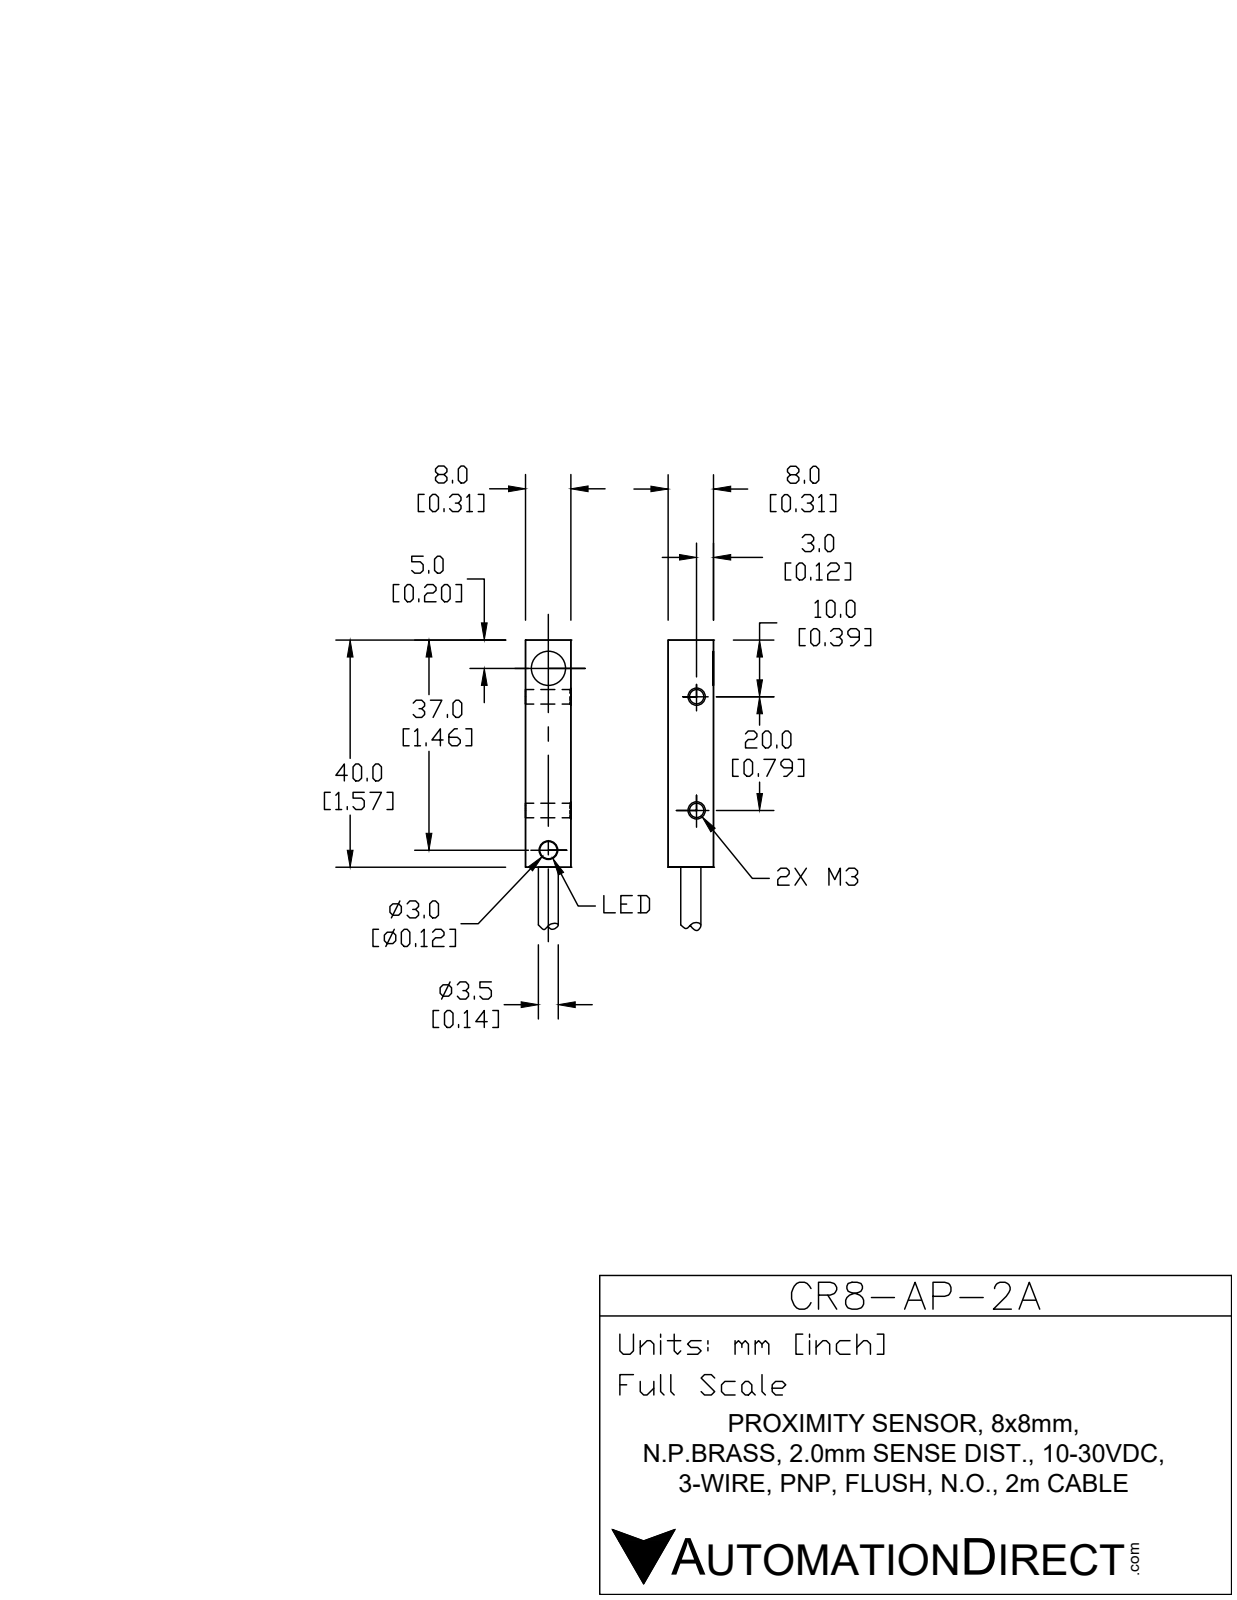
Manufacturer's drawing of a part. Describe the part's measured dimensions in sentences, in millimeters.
The part is named "CR8-AP-2A". Its 3-D file was written by "SolidWorks 2017 (AUTOMOTIVE_DESIGN)". It is 3 solids with 30 faces: 19 planar, 4 cylindrical and 7 other. Overall it measures 61.9 by 8 by 8 millimeters. Its volume is 2 870 cubic millimeters and its surface area 2 534 square millimeters. Round holes: 2 of diameter 2.5. Round bosses or shafts: 1 of diameter 3.5. Partial cylindrical surfaces (rounded edges, fillets, slot ends): 1 of radius 3.4. The main face-to-face distances are 8, 0.5, 7.5, 7.9, 0.4, 40, 7.4, 7.8, 7.9, 6. The hole center spacings are 20.
